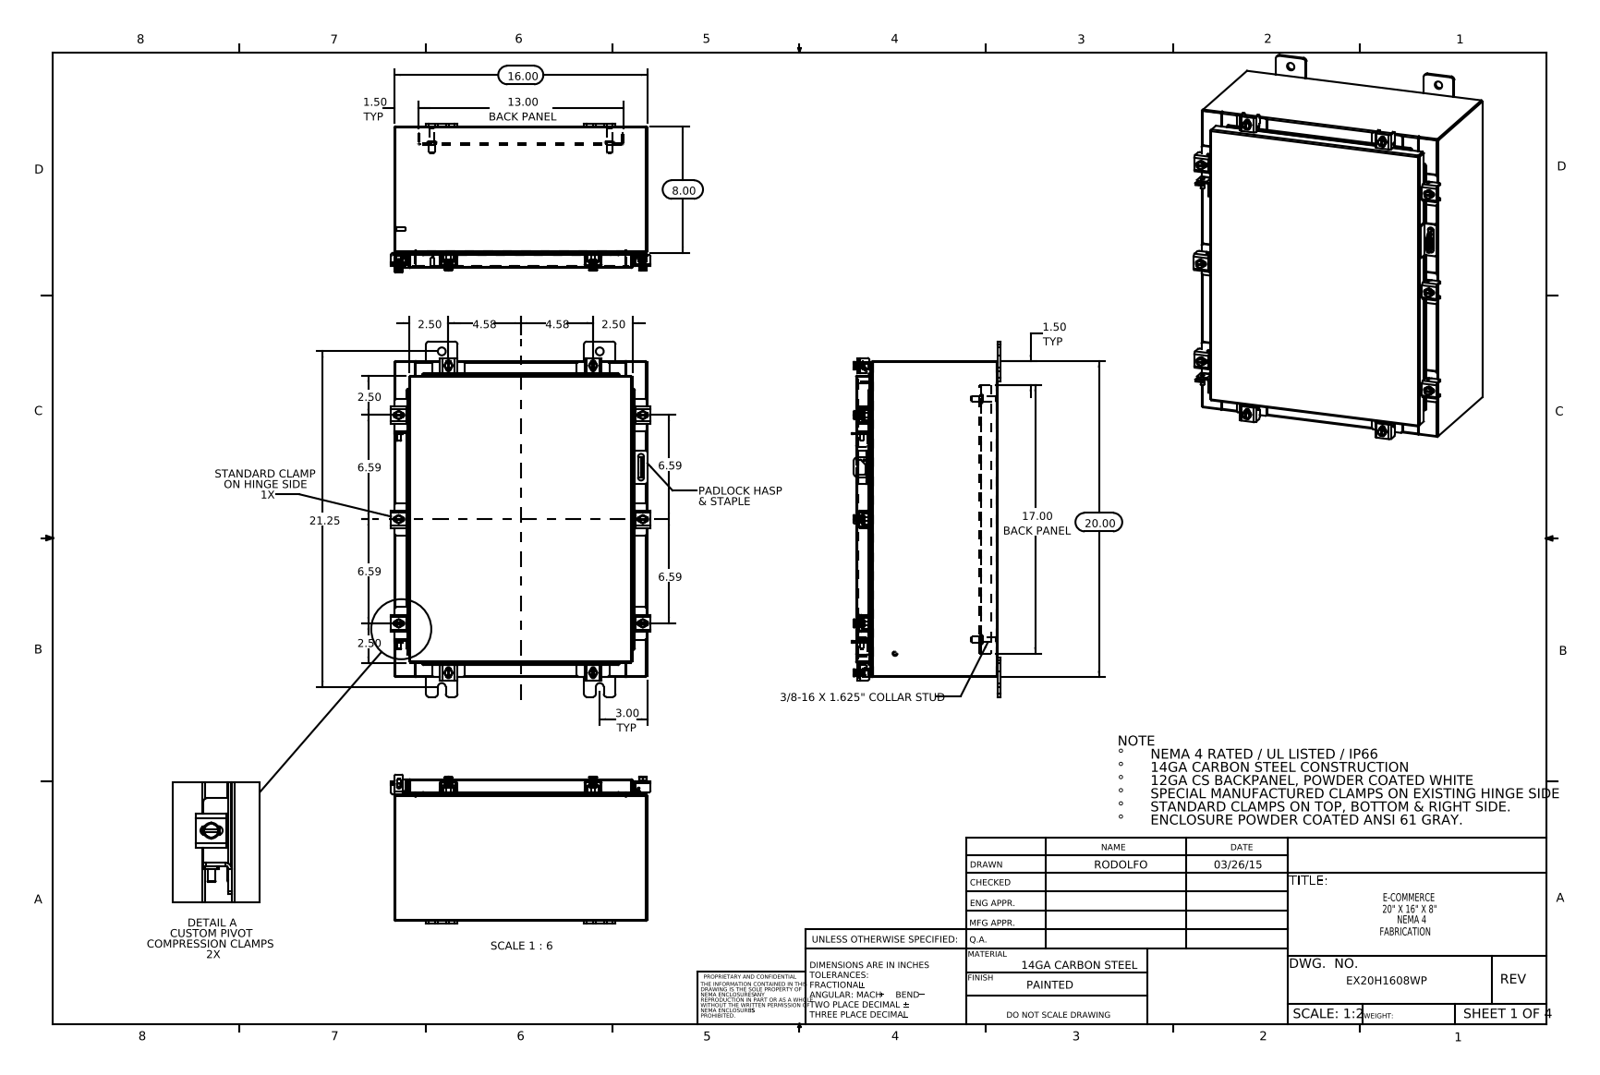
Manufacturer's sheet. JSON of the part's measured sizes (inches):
{"part_name": "30X10 Clamp Bracket2; Special Clamp Assembly; EX20H1608WP Bottom; EX20H1608WP Special Clamp (+8 more)", "step_written_by": "SolidWorks 2014 (CONFIG_CONTROL_DESIGN)", "units": "inches", "bodies": {"solids": 71, "faces": 1784, "planar": 955, "cylindrical": 685, "other": 144}, "overall_size": [22.5, 16.421, 9.453], "volume_in3": 135.4, "surface_area_in2": 3406, "round_holes": [[0.213, 10], [0.26, 10], [0.5, 8], [0.125, 1], [0.25, 1]], "round_bosses_or_shafts": [[0.5, 10], [0.25, 10], [0.399, 8], [0.625, 4], [0.375, 4], [0.33, 4], [0.315, 2], [0.236, 2]], "partial_cylinders_radius": [[0.06, 46], [0.013, 24], [0.19, 24], [0.088, 22], [0.141, 20], [0.12, 18], [0.09, 16], [0.1, 16]], "face_to_face_distances": [0.075, 8.9, 15.925, 8.975, 8.826, 19.925, 0.104, 1, 1.075, 7.826], "hole_center_spacings": [2.347, 4.44, 6.594, 10.222, 12.696, 14.374, 15.683, 16.62]}
